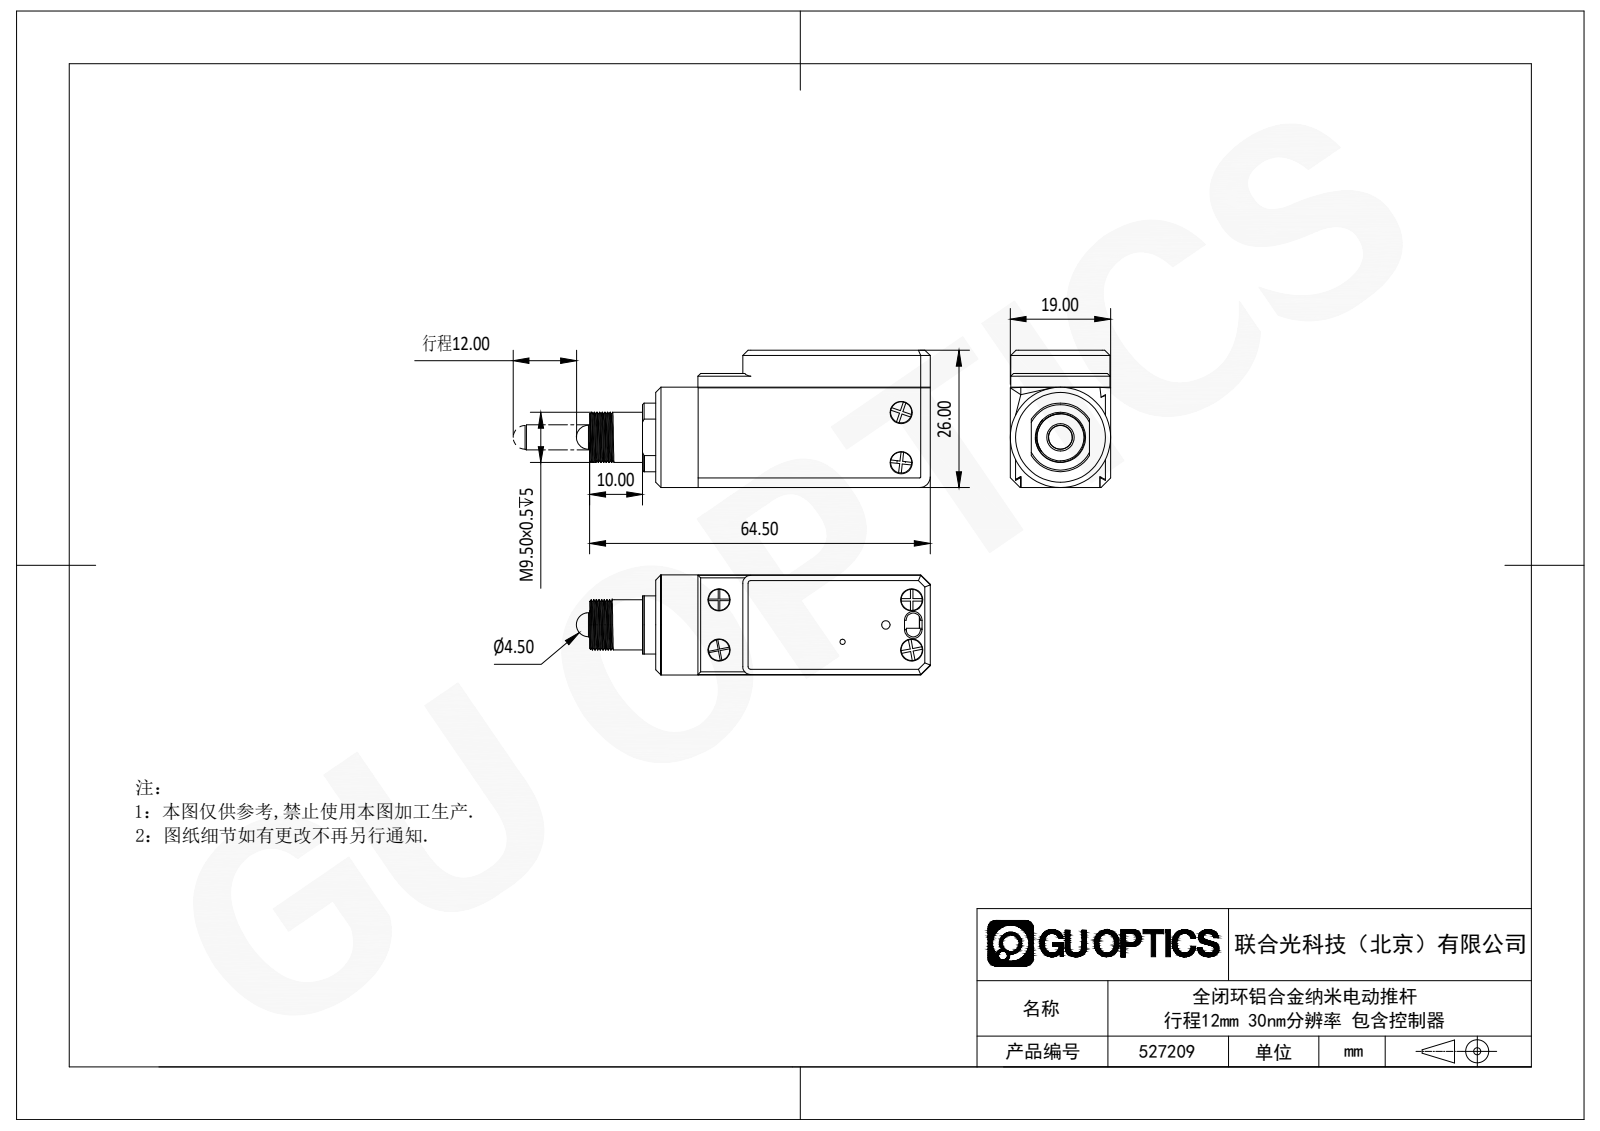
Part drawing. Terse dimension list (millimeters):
name: 527209
written by: SolidWorks 2020 (CONFIG_CONTROL_DESIGN)
unit: mm
bodies: 0 solids, 294 faces (198 planar, 74 cylindrical, 22 other)
size: 67 × 26 × 19
holes: 9× ⌀4.2, 1× ⌀1, 1× ⌀1.6, 1× ⌀4, 1× ⌀9.5, 1× ⌀19
bosses: 5× ⌀4, 1× ⌀5.2, 1× ⌀2.5
rounds: 6× R1.5, 2× R2, 1× R2.1, 1× R6.5
face distances: 1, 19, 17, 18.9, 18, 2, 1.9, 16, 0.9, 17.9
hole spacings: 9.5, 6.82, 7.27, 10.18, 27.91, 31.36, 31.96, 36.5
